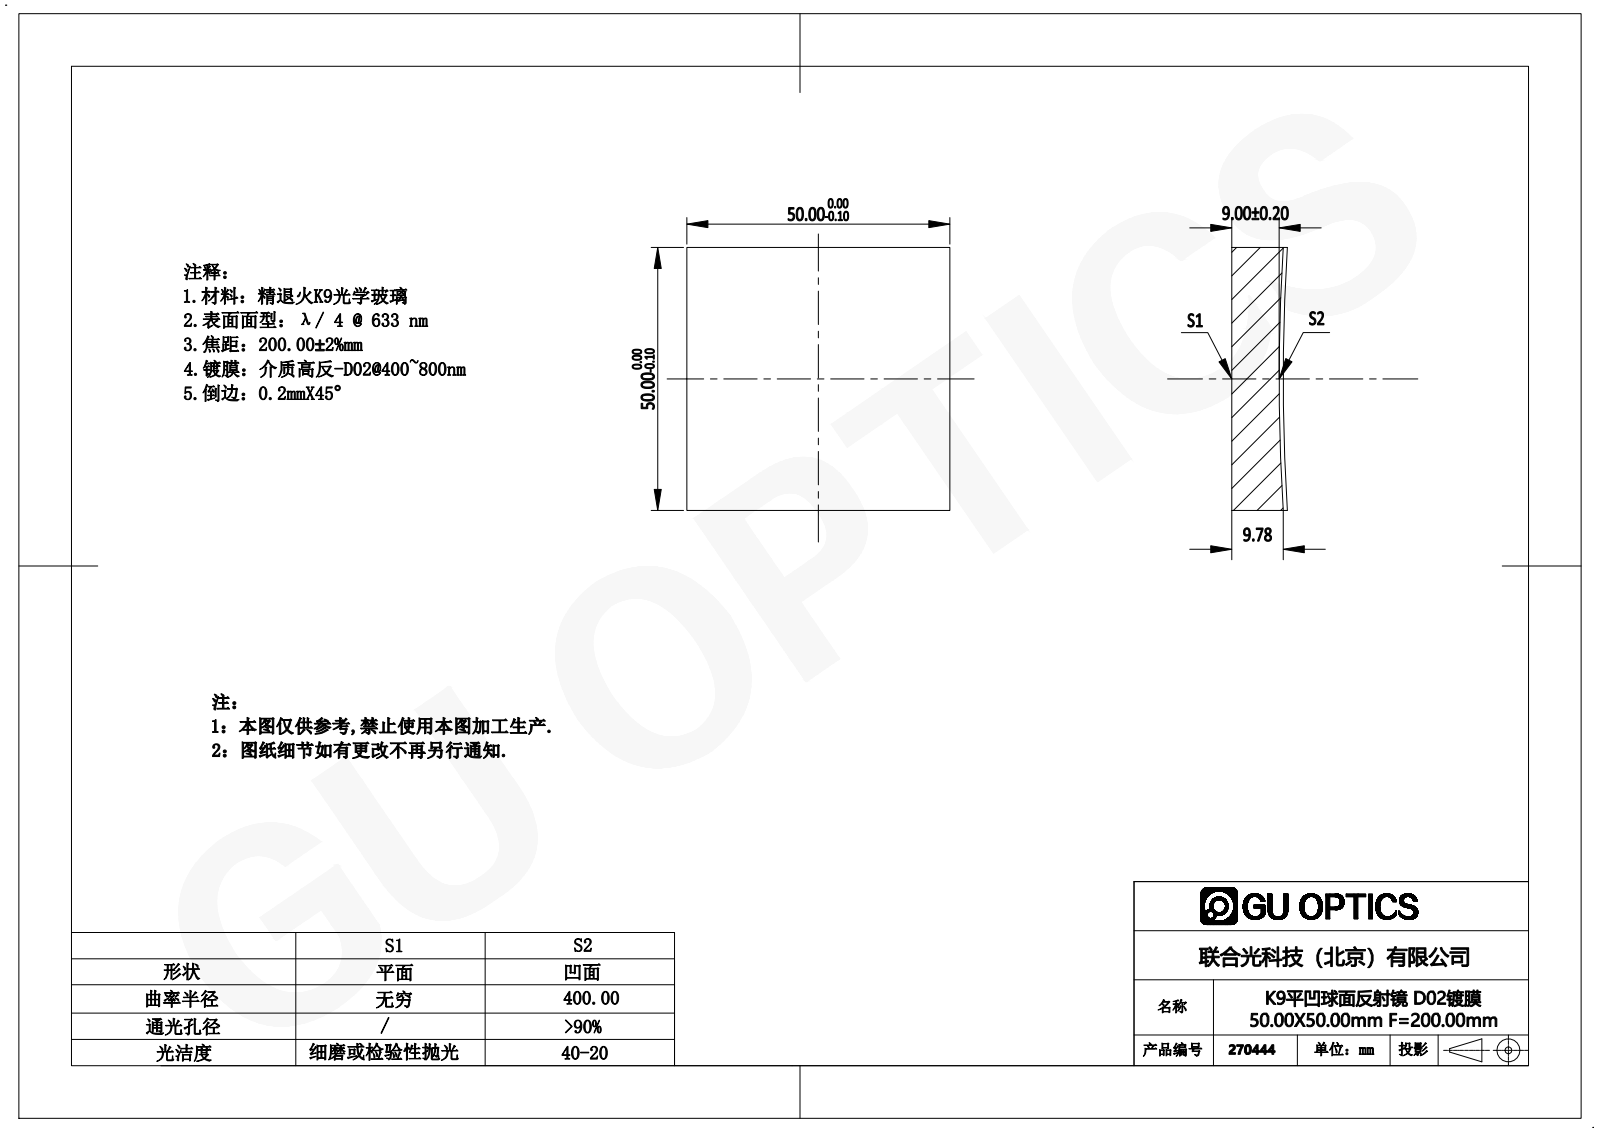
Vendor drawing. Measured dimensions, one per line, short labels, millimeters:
name: 270054
written by: SolidWorks 2019 (AUTOMOTIVE_DESIGN)
unit: mm
bodies: 1 solid, 7 faces (5 planar, 0 cylindrical, 2 other)
size: 50 × 50 × 10.57
volume: 23 803 mm³; area: 7 012 mm²
face distances: 50
